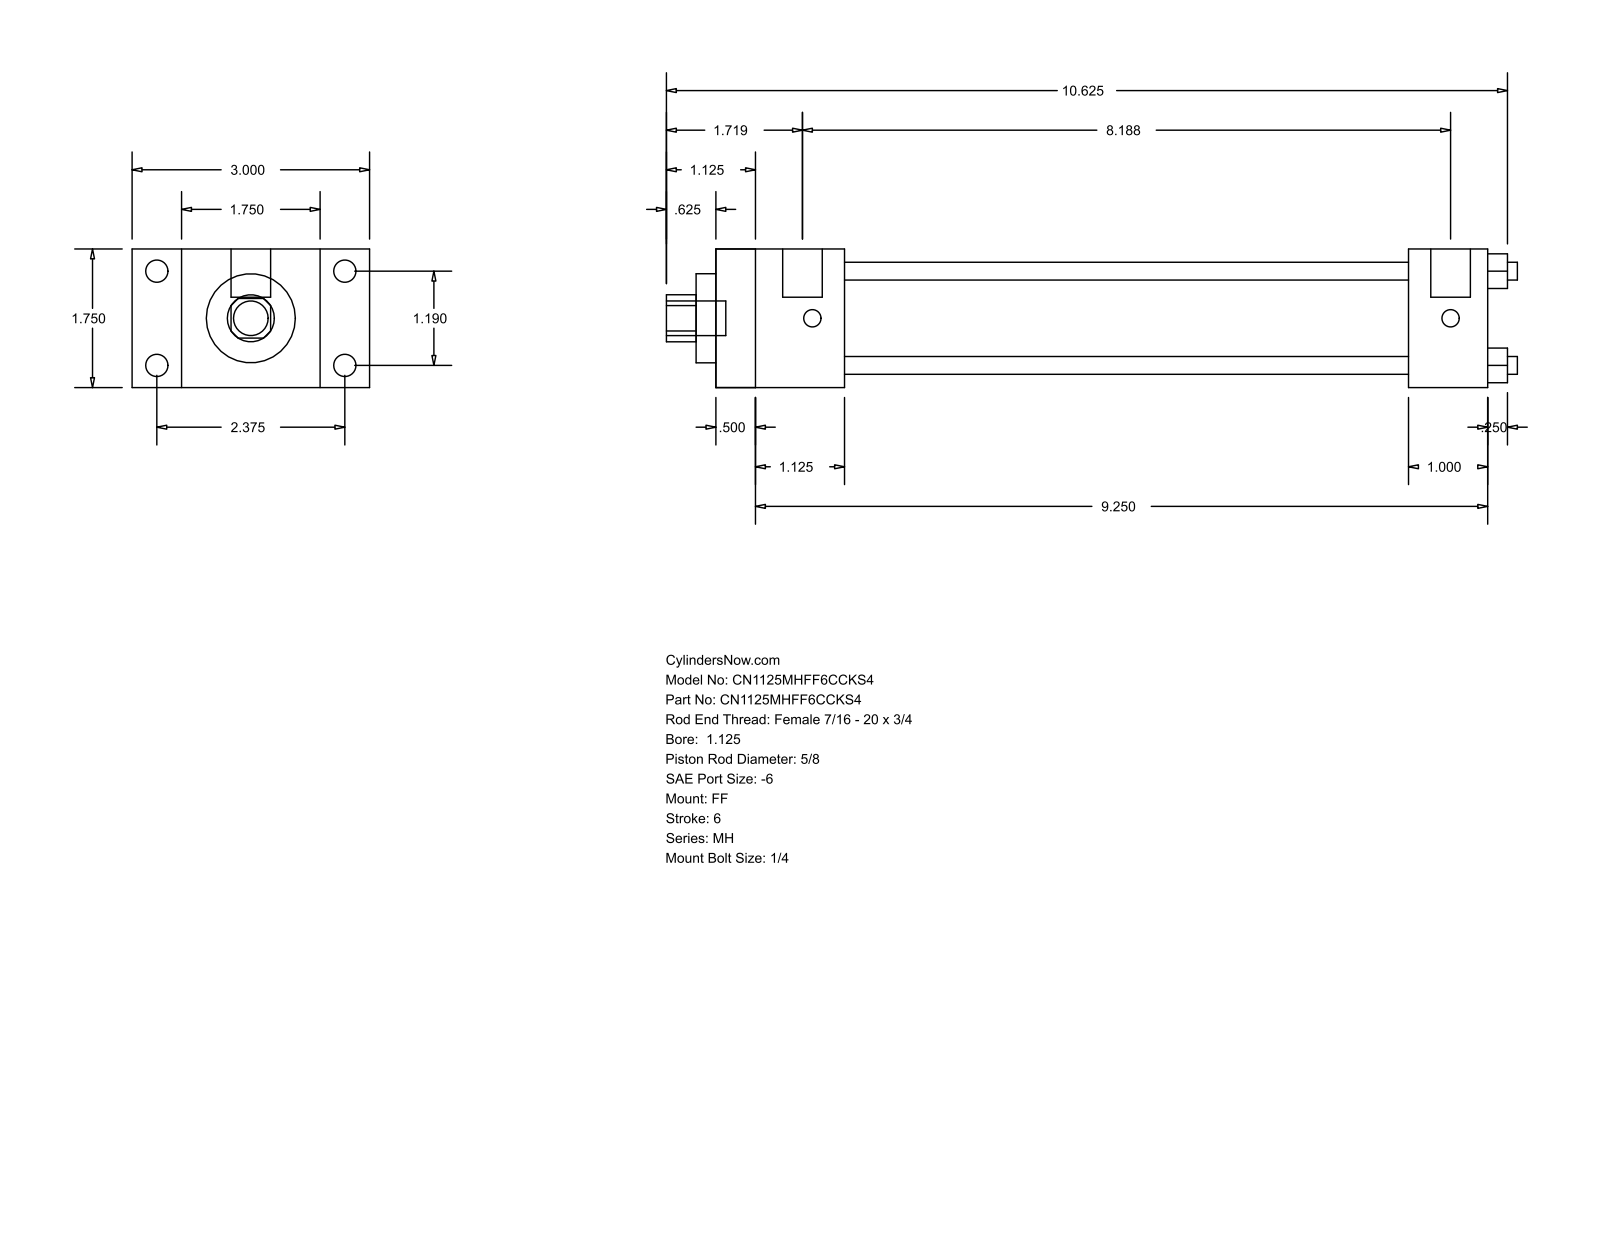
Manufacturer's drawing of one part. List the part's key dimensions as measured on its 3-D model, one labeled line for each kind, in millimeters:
Part name (STEP PRODUCT): MH_FF__0112_0.625
STEP written by: GSSL Pune (CONFIG_CONTROL_DESIGN)
Units: millimetres
Bodies: 0 solids, 92 faces (64 planar, 28 cylindrical, 0 other)
Overall size (bounding box): 273.05 × 76.2 × 44.45
Round holes (diameter × count): ⌀5.71 ×4, ⌀15.88 ×1, ⌀28.57 ×1, ⌀34.92 ×1
Round bosses / shafts (diameter × count): ⌀7.14 ×4, ⌀5.56 ×4, ⌀12.7 ×2, ⌀11.11 ×1
Partial cylindrical surfaces — rounded edges, fillets, slot ends (radius × count): R7.54 ×1
Main face-to-face distances: 44.46, 247.64, 12.69, 234.95, 15.87, 60.33, 28.58, 41.27, 222.24, 209.55
Hole centre spacings: 21.37, 30.22, 42.74
